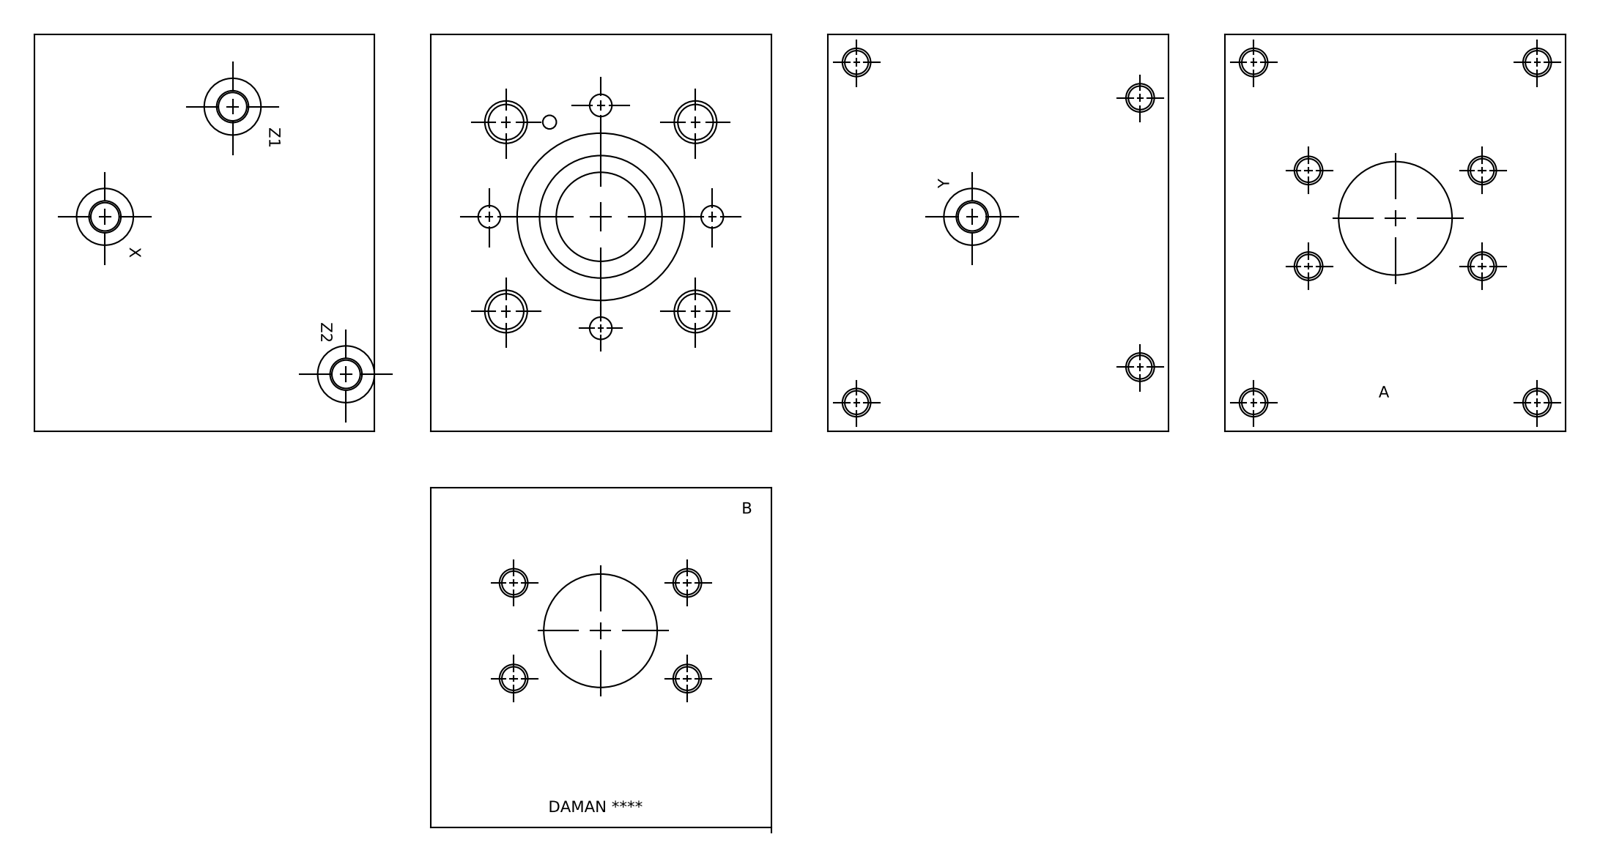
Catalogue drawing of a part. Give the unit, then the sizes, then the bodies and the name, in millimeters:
Units: millimetres
Overall size (bounding box): 177.8 × 152.4 × 152.4
Round holes (diameter × count): ⌀10.72 ×16, ⌀12.7 ×16, ⌀10.01 ×4, ⌀12.29 ×4, ⌀12.9 ×4, ⌀14.27 ×4, ⌀14.53 ×4, ⌀16.66 ×4, ⌀19.05 ×4, ⌀25.02 ×4, ⌀8 ×2, ⌀50.8 ×2
Main face-to-face distances: 152.4, 177.8, 86.99, 65.41, 0.79, 151.61, 47.42, 17.99, 104.98, 30.18
Hole centre spacings: 44.41, 43.17, 101.83, 24.15, 42.88, 48.26, 50.01, 70.72
Volume: 3 421 000 mm³ · Surface area: 227 030 mm²
Bodies: 1 solid, 584 faces (366 planar, 76 cylindrical, 142 other)
Part name (STEP PRODUCT): Part_A40XA32F61_3D
STEP written by: Autodesk Inventor 2020 (CONFIG_CONTROL_DESIGN)
